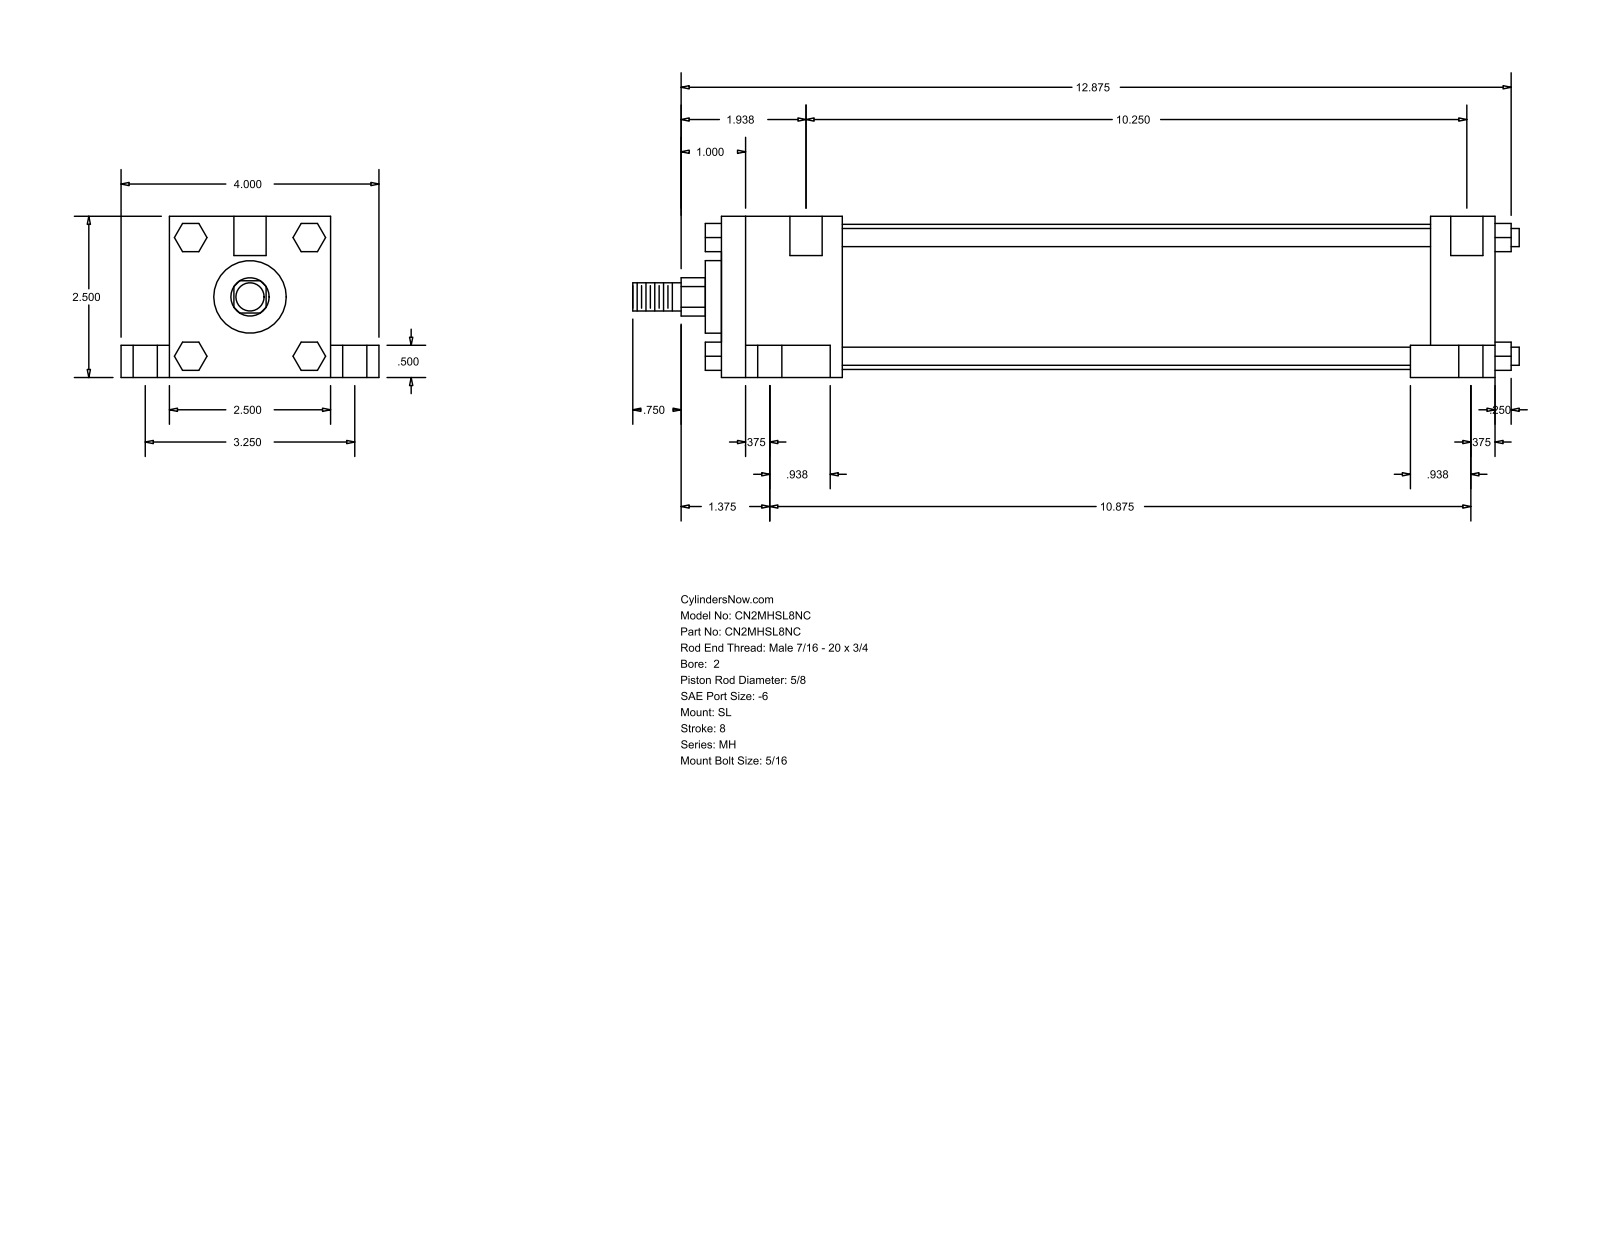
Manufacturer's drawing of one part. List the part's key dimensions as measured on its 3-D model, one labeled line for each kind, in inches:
Part name (STEP PRODUCT): MH_SL__0200_0.625
STEP written by: GSSL Pune (CONFIG_CONTROL_DESIGN)
Units: inches
Bodies: 0 solids, 148 faces (112 planar, 36 cylindrical, 0 other)
Overall size (bounding box): 13.75 × 4 × 2.5
Round holes (diameter × count): ⌀0.219 ×4, ⌀0.375 ×4, ⌀0.625 ×4, ⌀0.5 ×2
Round bosses / shafts (diameter × count): ⌀0.281 ×4, ⌀2.25 ×1, ⌀1.125 ×1, ⌀0.625 ×1, ⌀0.437 ×1
Partial cylindrical surfaces — rounded edges, fillets, slot ends (radius × count): R0.297 ×1
Main face-to-face distances: 2.5, 12, 0.5, 0.75, 3.25, 2, 11, 1, 1.875, 9.125
Hole centre spacings: 1.626, 1.668, 1.719, 3.25, 10.44, 10.563, 10.625, 10.875
